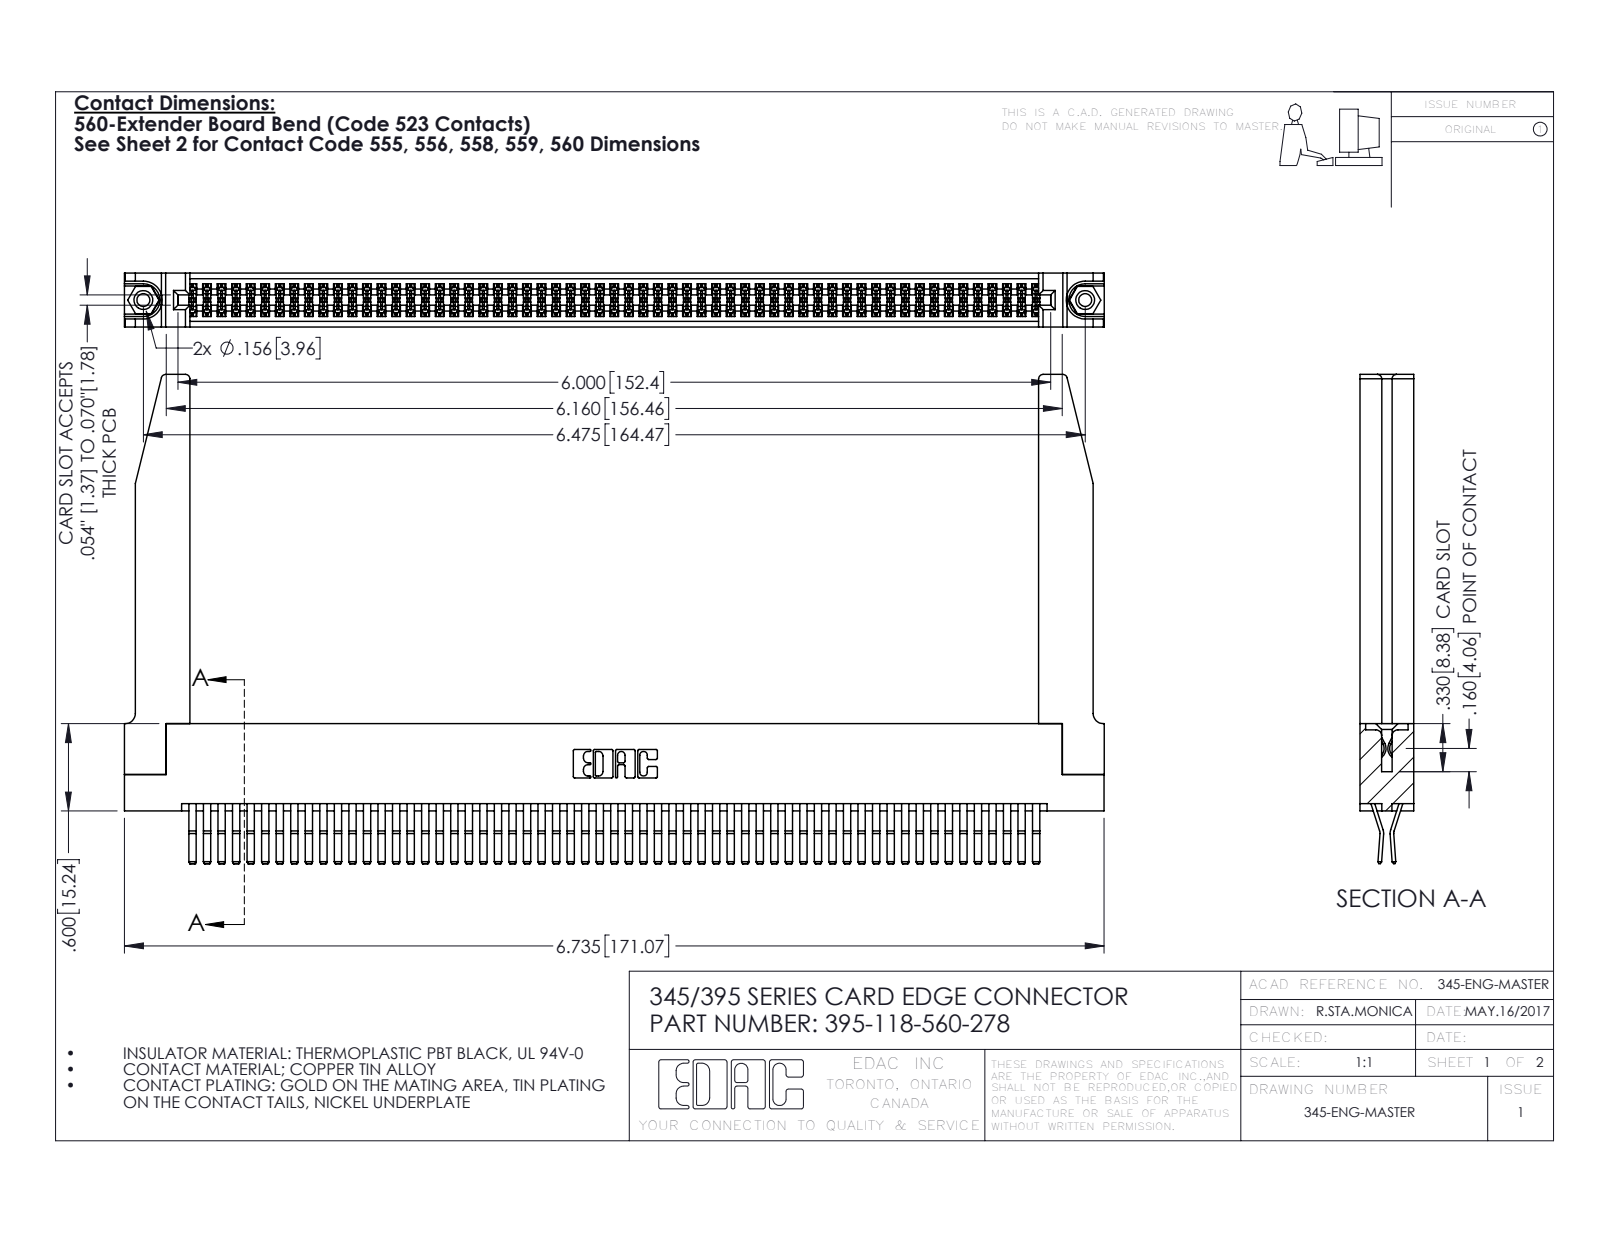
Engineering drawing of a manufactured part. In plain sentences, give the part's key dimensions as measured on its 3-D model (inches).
The part is named "345-250-001_345-250-001-102; 345 Part_Flush Mounting Lugs - 0.156 Dia-TH; 395-118-560-278; 345-292-001_560 Tail (+1 more)". Its 3-D file was written by "SolidWorks 2016 (CONFIG_CONTROL_DESIGN)". It is 123 solids with 6496 faces: 4116 planar, 2328 cylindrical and 52 other. Overall it measures 6.736 by 3.362 by 0.37 inches. Its volume is 1.545 cubic inches and its surface area 54.41 square inches. Round holes: 2 of diameter 0.089, 2 of diameter 0.125, 2 of diameter 0.156, 1 of diameter 0.064. Round bosses or shafts: 2 of diameter 0.155. Partial cylindrical surfaces (rounded edges, fillets, slot ends): 177 of radius 0.006, 22 of radius 0.01, 8 of radius 0.03, 6 of radius 0.007, 6 of radius 0.031, 3 of radius 0.026, 2 of radius 0.01, 2 of radius 0.014. The main face-to-face distances are 0.072, 0.37, 0.298, 0.025, 0.2, 0.098, 0.272, 0.225, 0.175, 0.148. The hole center spacings are 0.27, 6.239, 6.475.
